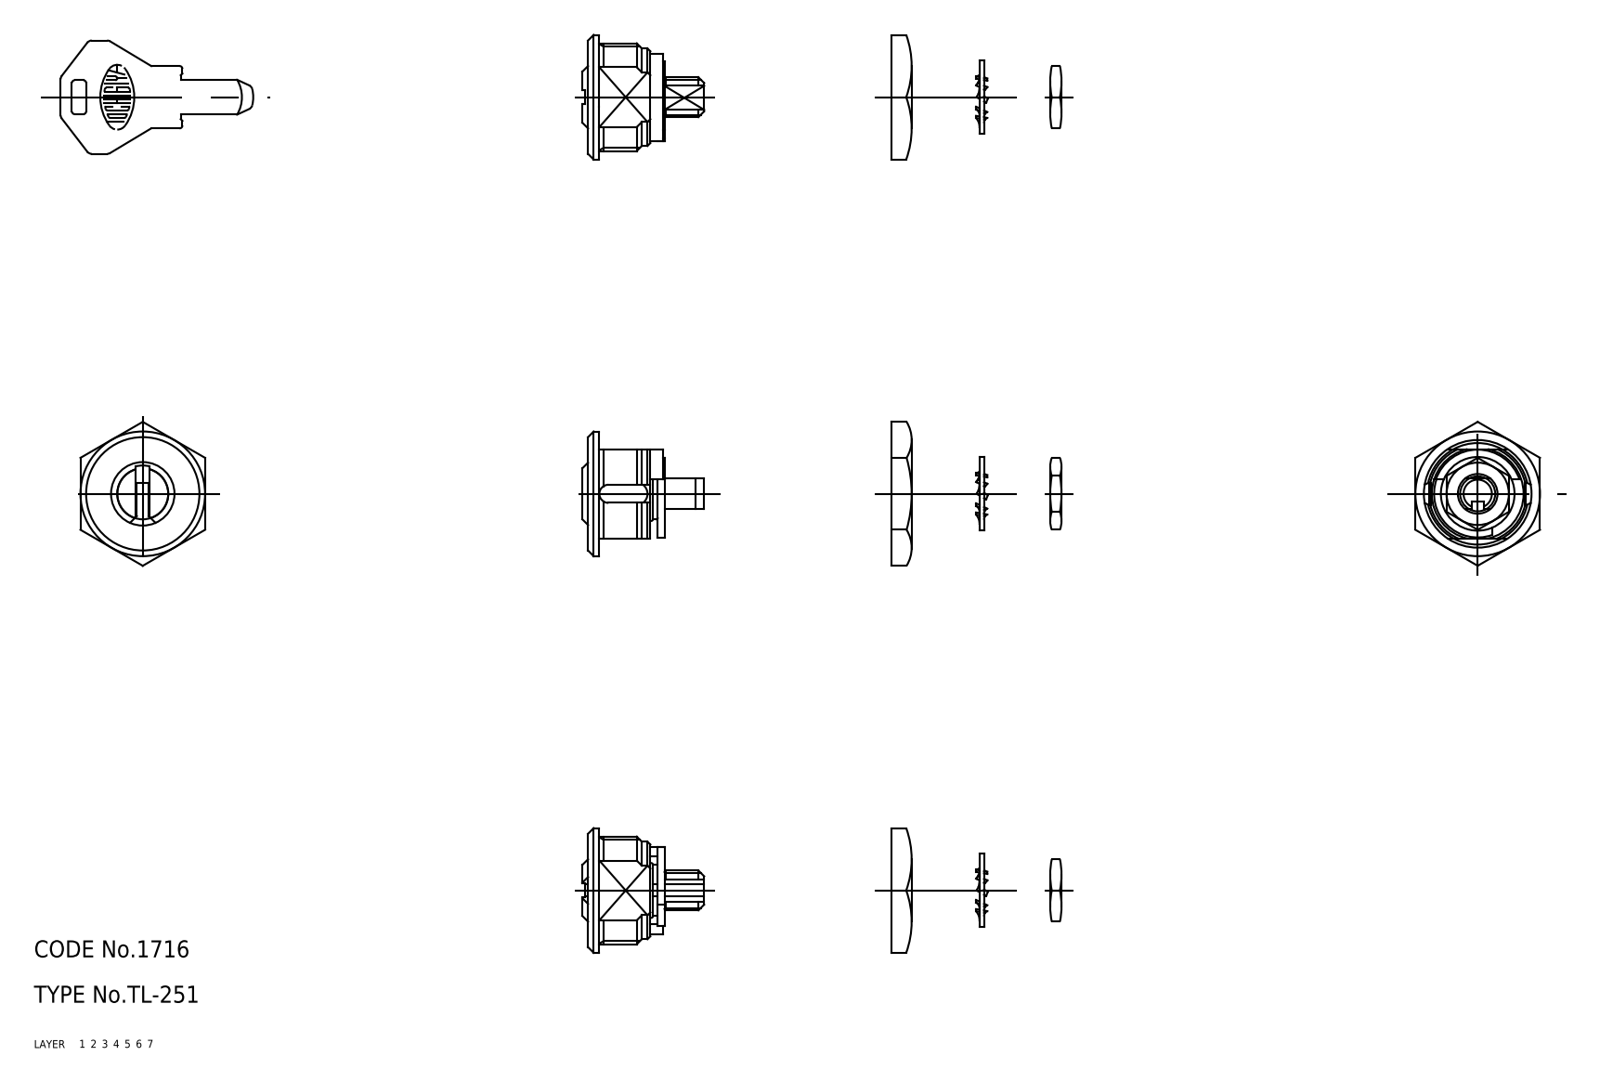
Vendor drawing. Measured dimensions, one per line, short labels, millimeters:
name: washer; nut_B; nut_A; lock (+3 more)
written by: CADfix (AUTOMOTIVE_DESIGN)
unit: mm
bodies: 6 solids, 156 faces (0 planar, 0 cylindrical, 156 other)
size: 75.5 × 25.4 × 22
volume: 4 923 mm³; area: 4 179 mm²
